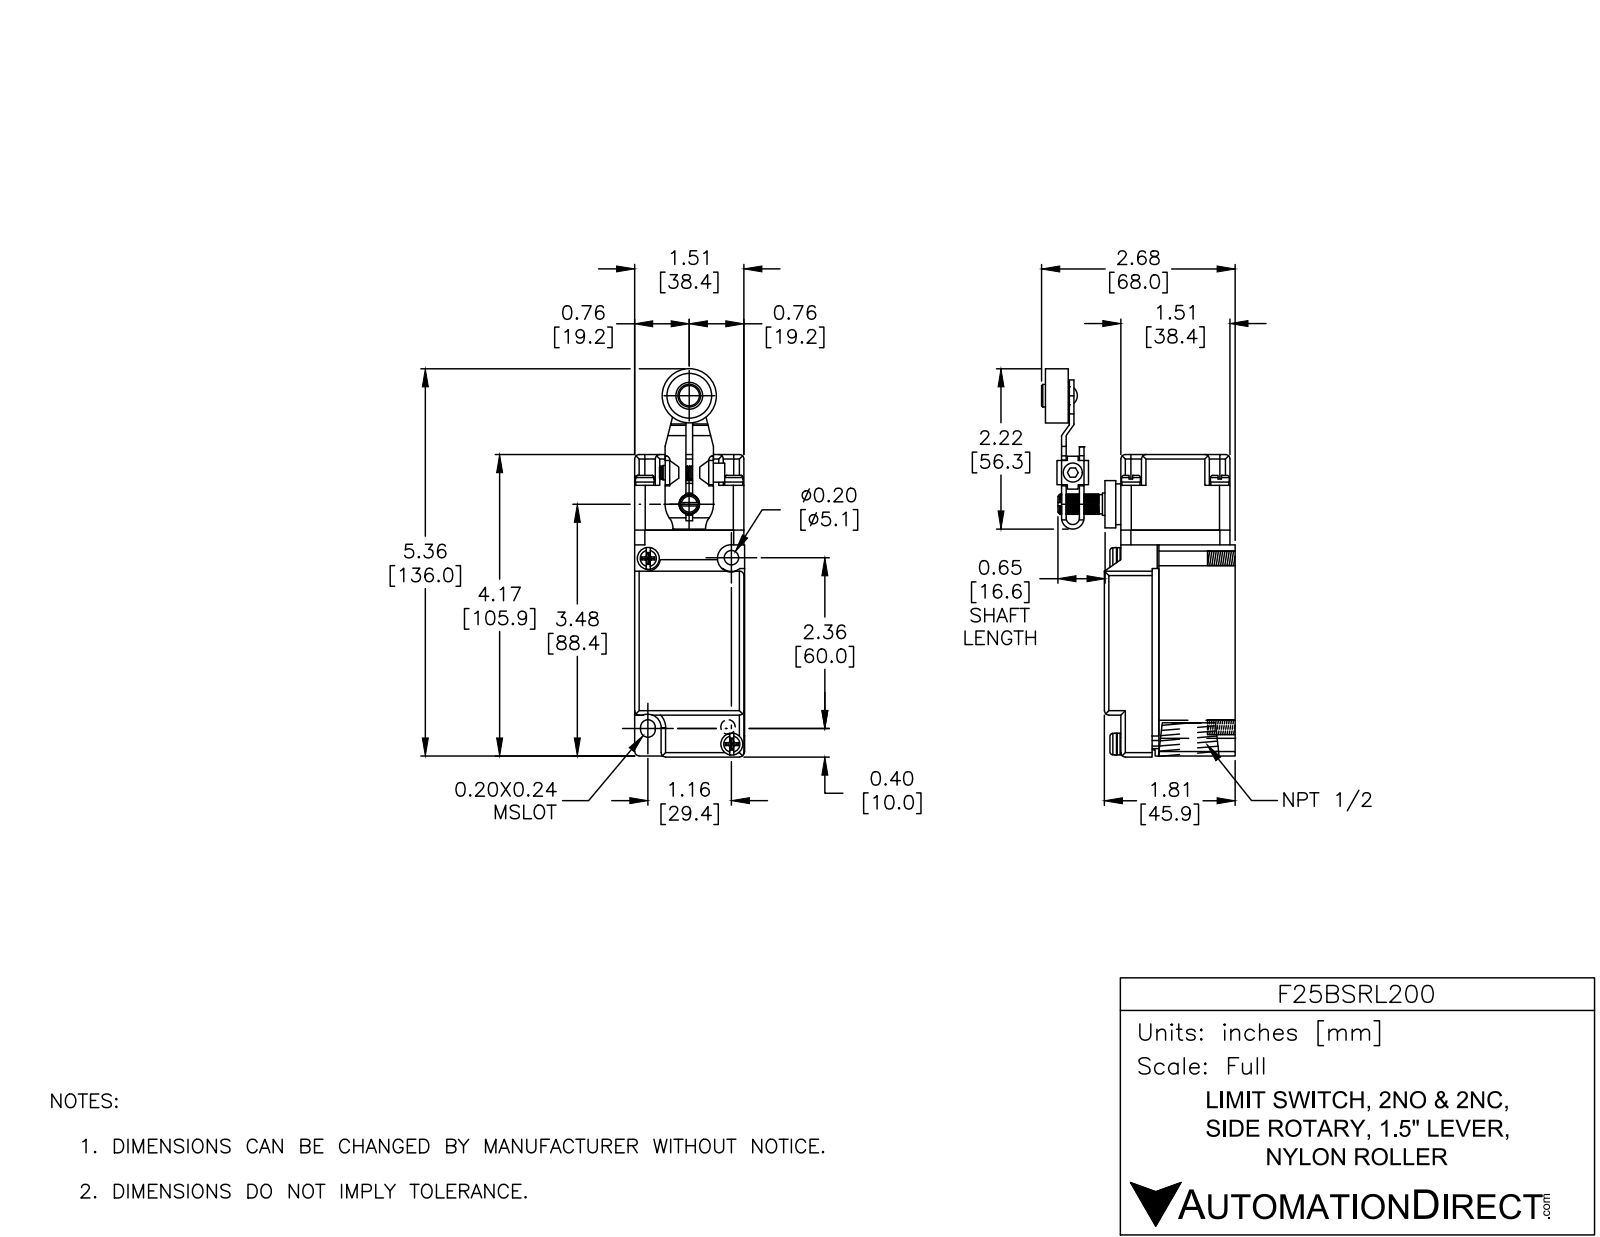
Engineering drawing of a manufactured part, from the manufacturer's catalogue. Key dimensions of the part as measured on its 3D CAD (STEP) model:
Part name (STEP PRODUCT): F25ASRL200; Imported74; Imported70; Imported73 (+8 more)
STEP written by: SolidWorks 2002296 (CONFIG_CONTROL_DESIGN)
Units: inches
Bodies: 17 solids, 929 faces (513 planar, 235 cylindrical, 181 other)
Overall size (bounding box): 5.371 × 2.678 × 1.52
Volume: 10.35 in³ · Surface area: 73.81 in²
Round holes (diameter × count): ⌀0.177 ×4, ⌀0.19 ×3, ⌀0.2 ×3, ⌀0.156 ×1, ⌀0.17 ×1, ⌀0.251 ×1, ⌀0.58 ×1, ⌀0.62 ×1
Round bosses / shafts (diameter × count): ⌀0.26 ×4, ⌀0.25 ×4, ⌀0.302 ×2, ⌀0.3 ×2, ⌀0.75 ×1, ⌀0.655 ×1, ⌀0.565 ×1, ⌀0.375 ×1
Partial cylindrical surfaces — rounded edges, fillets, slot ends (radius × count): R0.062 ×29, R0.03 ×16, R0.015 ×8, R0.145 ×8, R0.063 ×4, R0.14 ×4, R0.032 ×3, R0.025 ×2
Main face-to-face distances: 0.094, 1.149, 1.055, 1.52, 0.66, 0.754, 1.809, 1.51, 0.227, 0.433
Hole centre spacings: 1.23, 1.23, 1.74, 2.815, 0.225, 0.235, 0.936, 0.942
